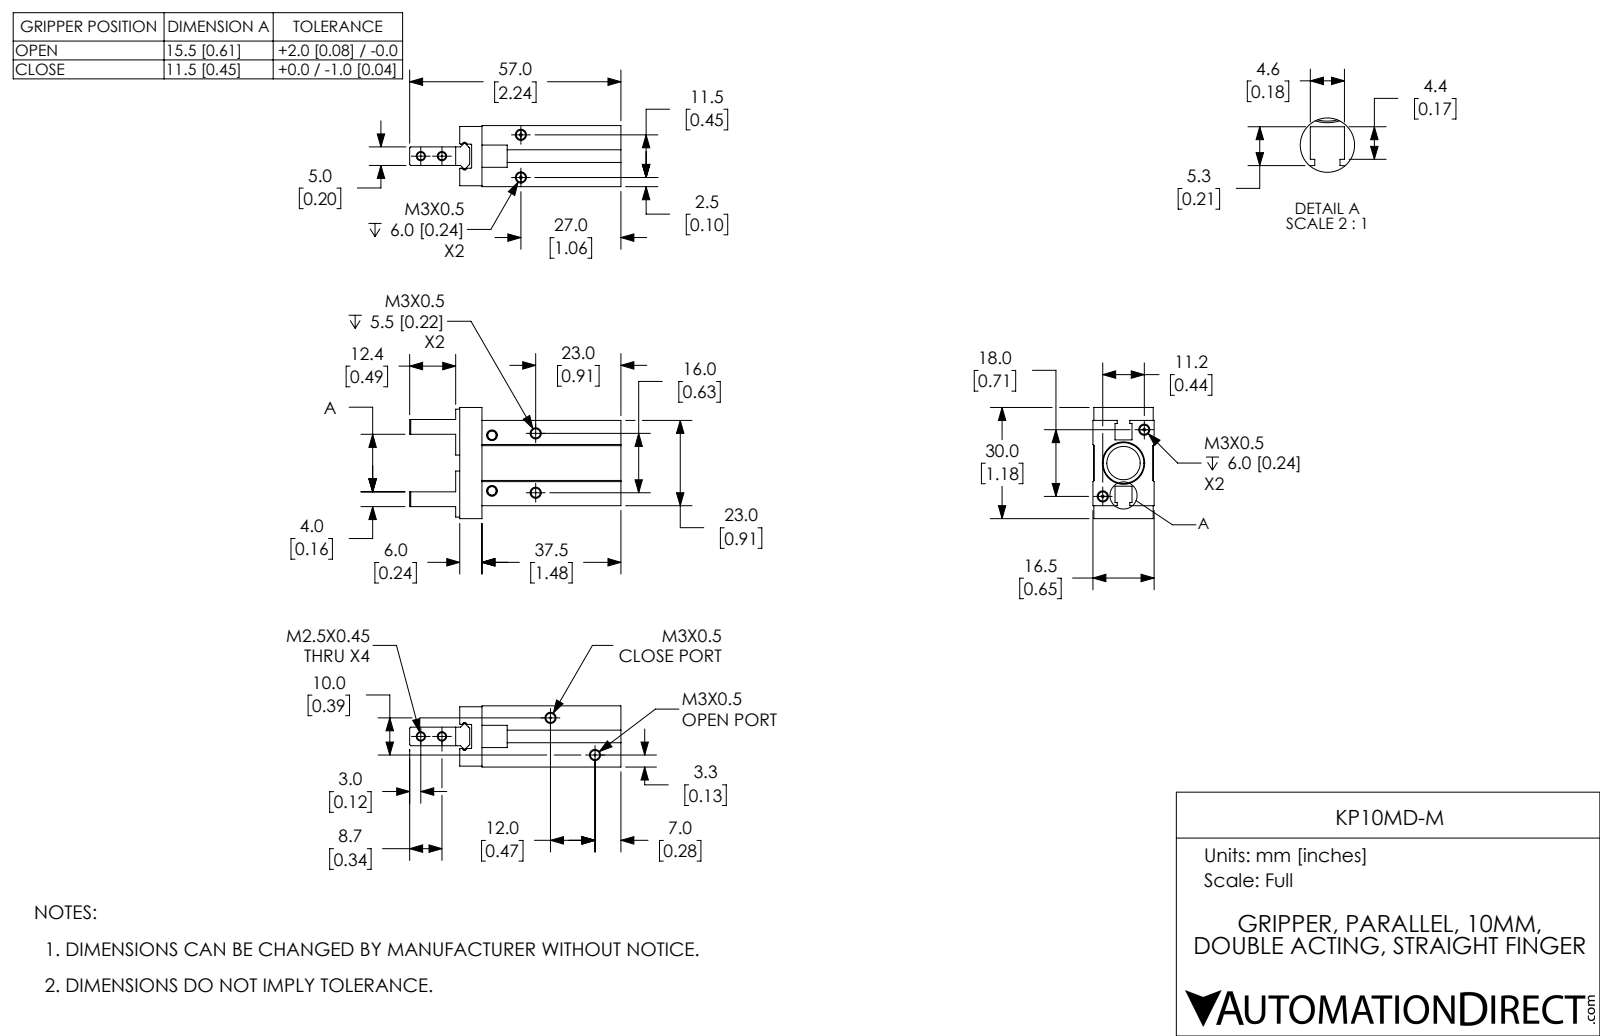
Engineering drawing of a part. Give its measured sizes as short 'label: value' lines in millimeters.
name: KP10MD-M; KP10MD-M-3; KP10MD-M-2; KP10MD-M-1
written by: SolidWorks 2017 (CONFIG_CONTROL_DESIGN)
unit: mm
bodies: 3 solids, 228 faces (110 planar, 56 cylindrical, 62 other)
size: 57 × 30 × 16.5
volume: 14 341 mm³; area: 7 450 mm²
holes: 4× ⌀2.46, 4× ⌀2.46, 2× ⌀0.5, 2× ⌀2.01, 2× ⌀3.02, 1× ⌀9, 1× ⌀11
rounds: 4× R0.2, 2× R0.25, 2× R0.75
face distances: 16.2, 5.5, 5.25, 5, 5.65, 5.95, 10.55, 10.25, 16.5, 23
hole spacings: 10.6, 22.06, 27.61, 5.7, 8.04, 11.5, 13.4, 15.62
